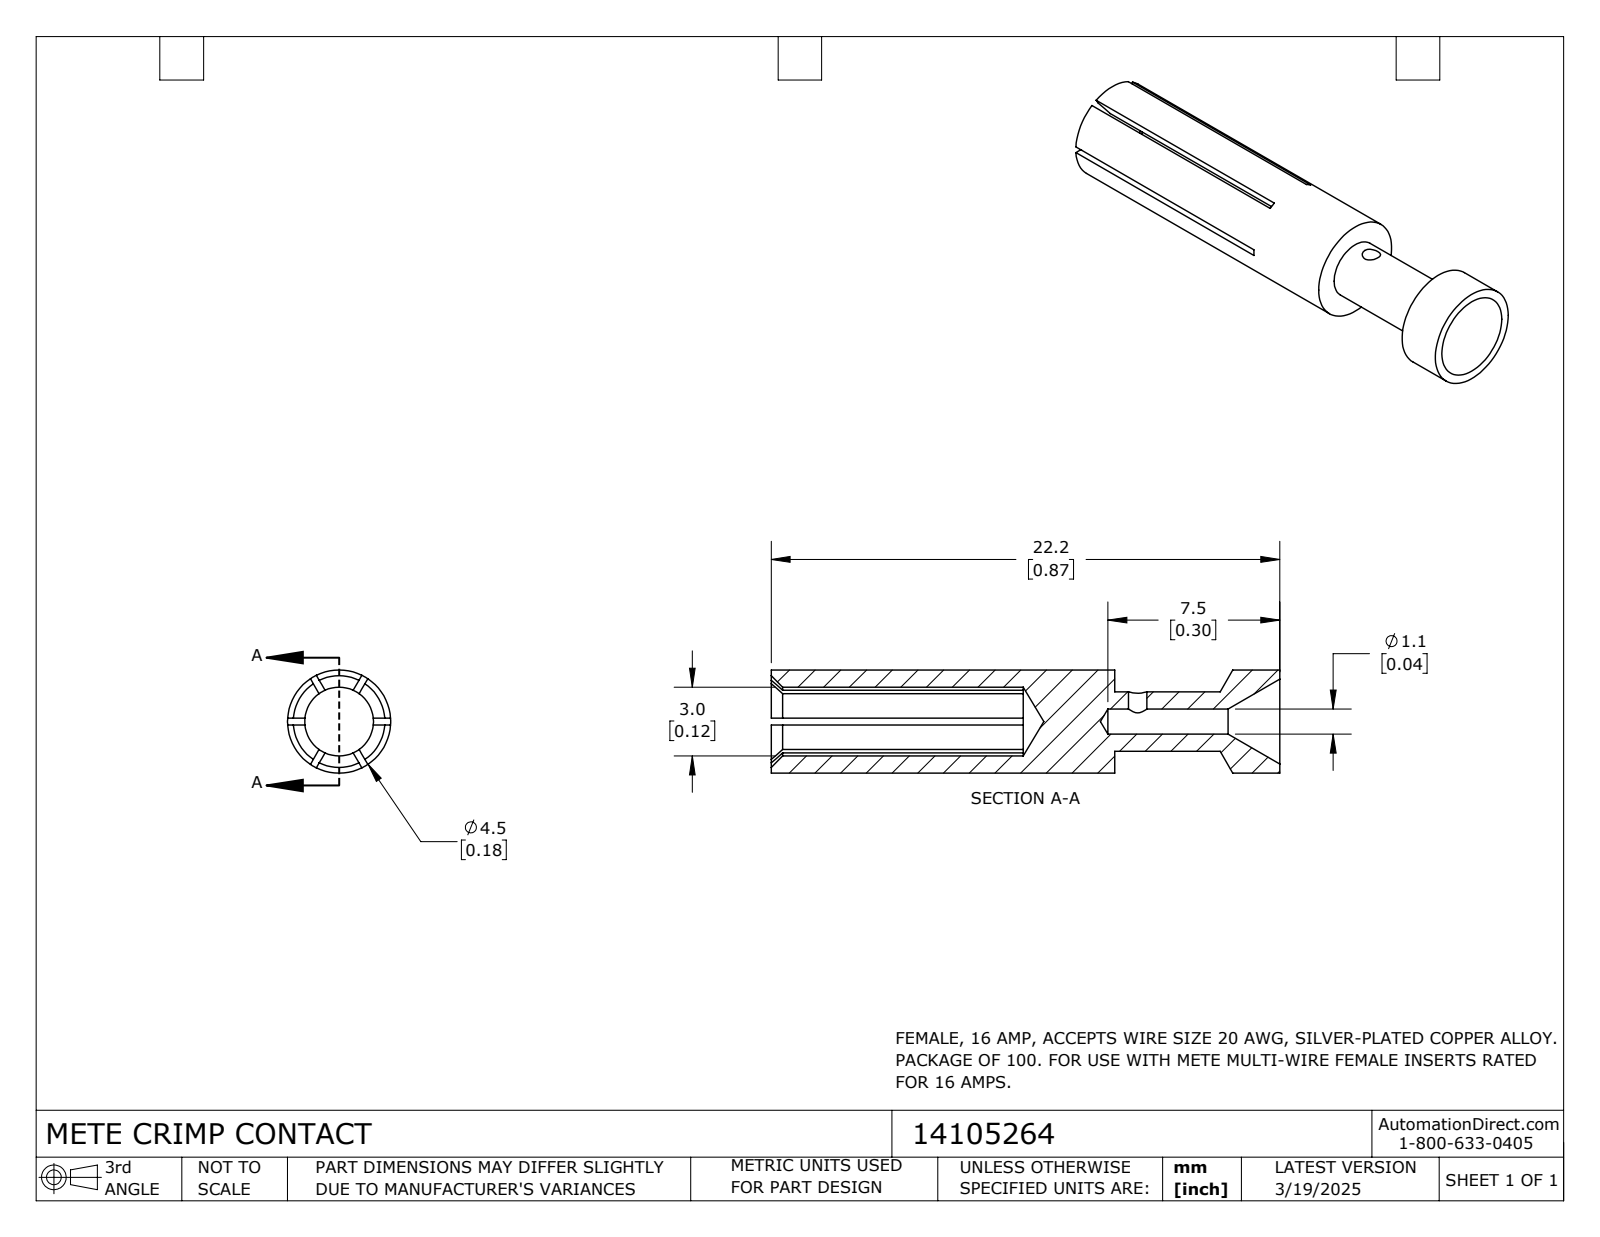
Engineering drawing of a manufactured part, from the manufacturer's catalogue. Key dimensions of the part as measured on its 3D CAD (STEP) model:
Part name (STEP PRODUCT): 14105264
STEP written by: SolidWorks 2024 (CONFIG_CONTROL_DESIGN)
Units: millimetres
Bodies: 1 solid, 56 faces (26 planar, 16 cylindrical, 14 other)
Overall size (bounding box): 22.2 × 4.5 × 4.5
Volume: 189 mm³ · Surface area: 523 mm²
Round holes (diameter × count): ⌀0.8 ×1, ⌀1.1 ×1, ⌀3 ×1
Round bosses / shafts (diameter × count): ⌀4.5 ×1, ⌀2.6 ×1
Main face-to-face distances: 7.2, 22.2, 15, 11.2, 4, 11
